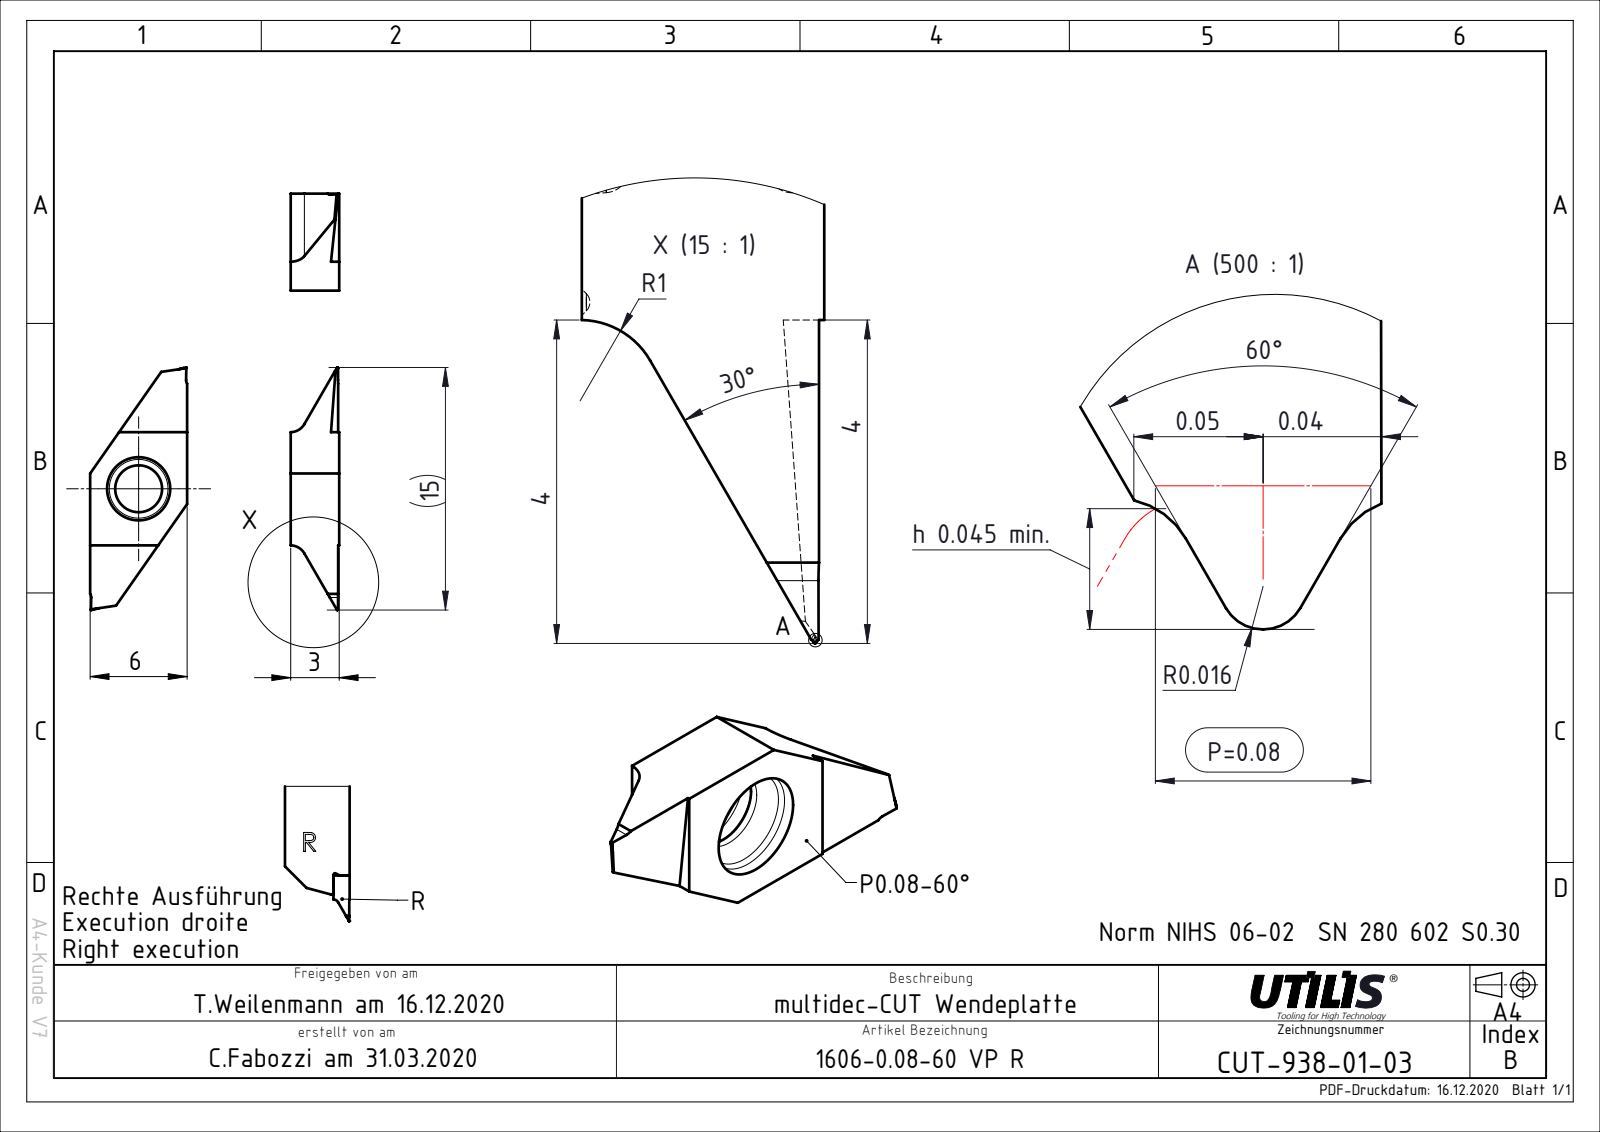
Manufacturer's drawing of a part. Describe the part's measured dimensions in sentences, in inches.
The part is named "CUT-938-01; ASME Y14.5". Its 3-D file was written by "FormatWorks Professional (AP242_MANAGED_MODEL_BASED_3D_ENGINEERING_MIM_LF)". It is 1 solid with 36 faces: 22 planar, 14 cylindrical and 0 other. Overall it measures 0.591 by 0.236 by 0.118 inches. Its volume is 0.008 cubic inches and its surface area 0.322 square inches. Round holes: 1 of diameter 0.114. Partial cylindrical surfaces (rounded edges, fillets, slot ends): 2 of radius 0.039. The main face-to-face distances are 0.236, 0.118, 0.354, 0.276, 0.472, 0.283, 0.283.
